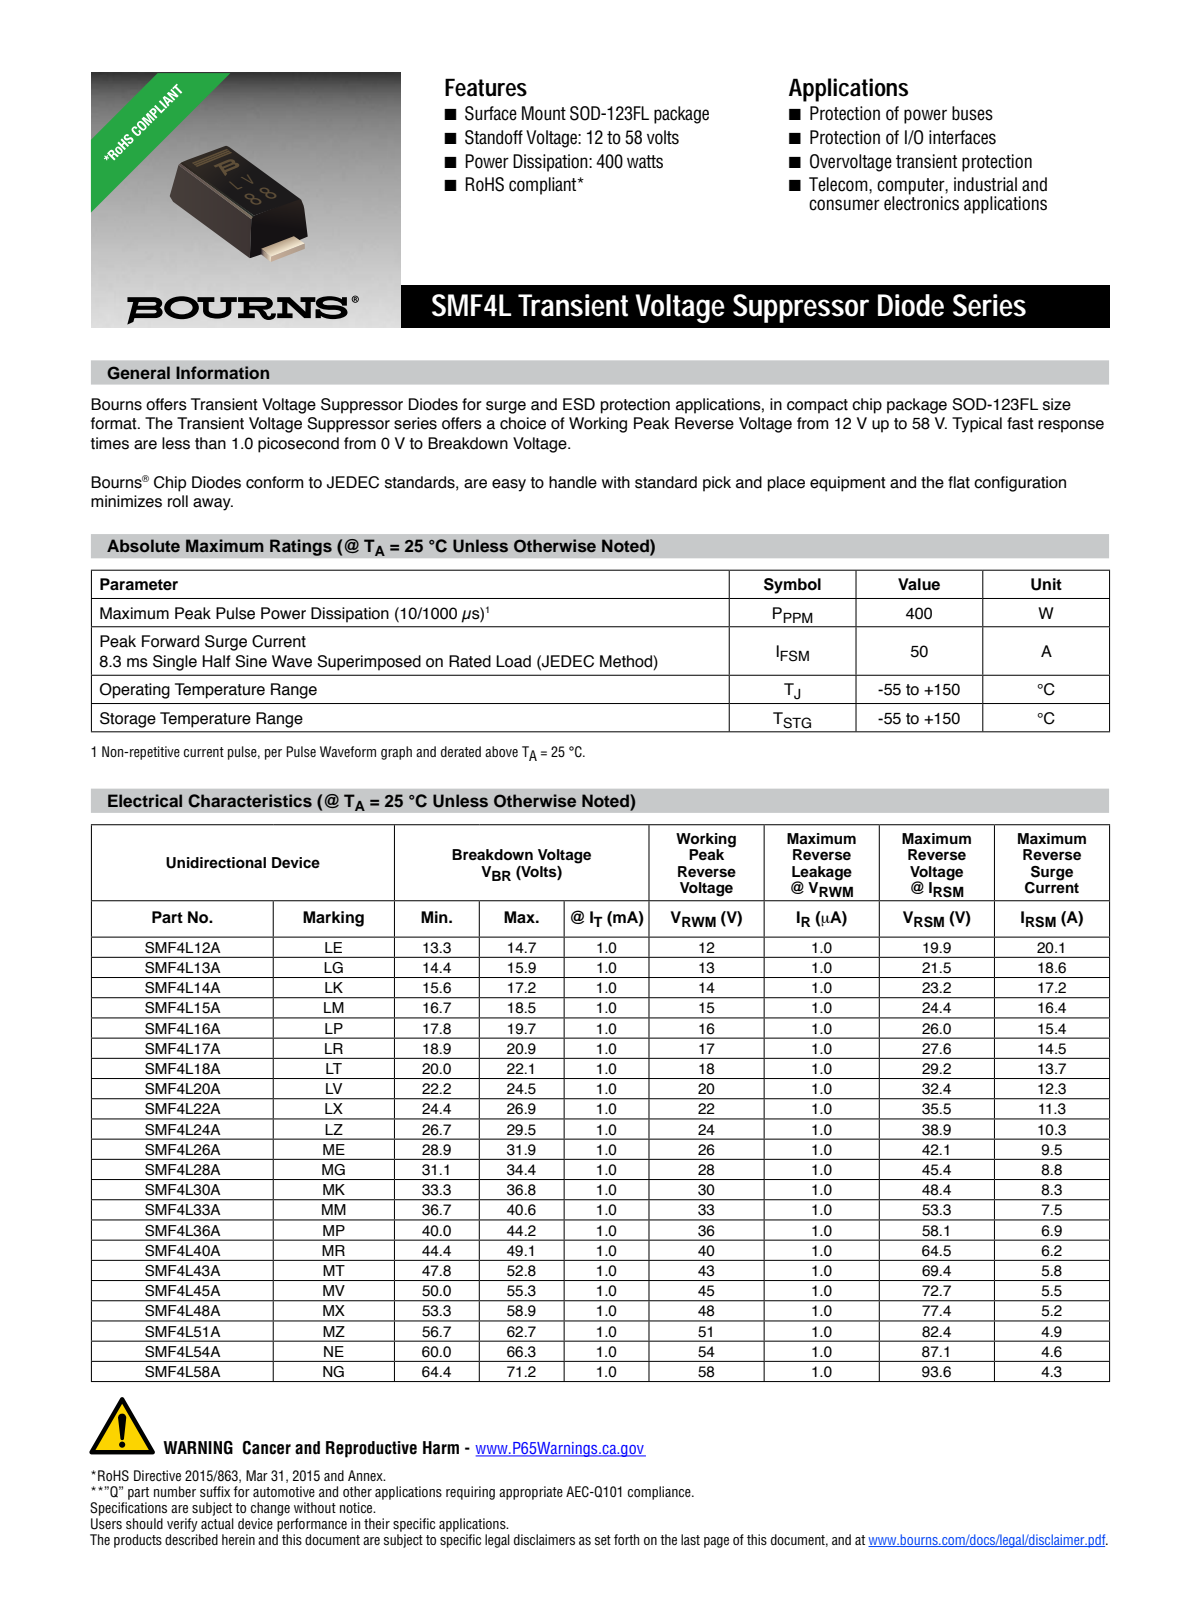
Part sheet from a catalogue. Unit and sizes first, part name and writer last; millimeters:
Units: millimetres
Overall size (bounding box): 3.7 × 1.7 × 1
Volume: 5 mm³ · Surface area: 22 mm²
Bodies: 3 solids, 26 faces (0 planar, 0 cylindrical, 26 other)
Part name (STEP PRODUCT): SOD123; SOD123001; SOD123002
STEP written by: FreeCAD (AUTOMOTIVE_DESIGN_CC2)
